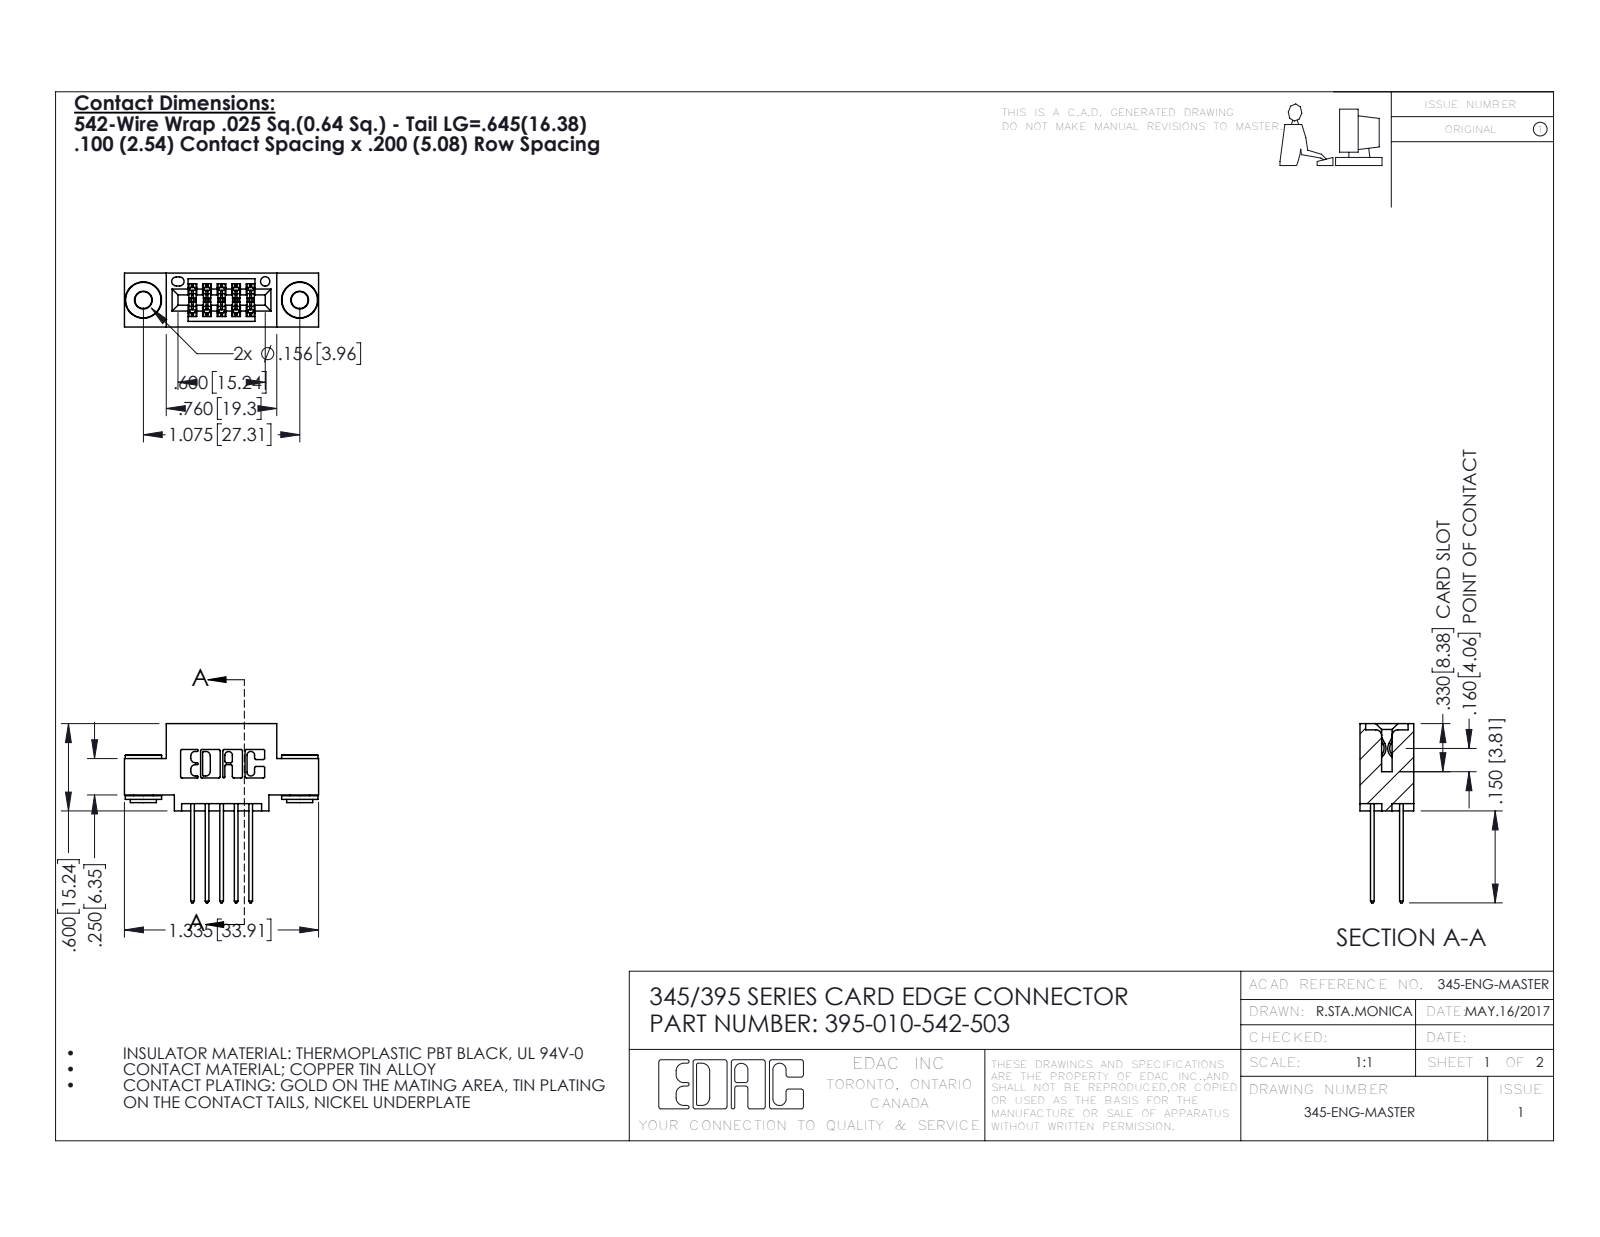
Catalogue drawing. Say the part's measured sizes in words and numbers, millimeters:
The part is named "395-010-542-503; 345 Part_0.110 Offset - 0.156 Dia-TH; 345-292-001_345-293-142; 345-250-002_345-250-002-102". Its 3-D file was written by "SolidWorks 2016 (CONFIG_CONTROL_DESIGN)". It is 13 solids with 668 faces: 424 planar, 236 cylindrical and 8 other. Overall it measures 33.9 by 31.3 by 9.4 millimeters. Its volume is 2 950 cubic millimeters and its surface area 4 150 square millimeters. Round holes: 2 of diameter 2.9, 2 of diameter 4, 1 of diameter 1.6. Round bosses or shafts: 2 of diameter 6.4, 2 of diameter 4.6, 2 of diameter 3.5. Partial cylindrical surfaces (rounded edges, fillets, slot ends): 22 of radius 0.3, 15 of radius 0.2, 10 of radius 0.3, 6 of radius 0.2, 6 of radius 0.8, 3 of radius 0.7, 2 of radius 0.4, 2 of radius 0.5. The main face-to-face distances are 5.1, 1.8, 7.6, 0.6, 9.4, 2.5, 2.5, 6.9, 6.4, 5.7. The hole center spacings are 6.9, 21.5, 27.3.
